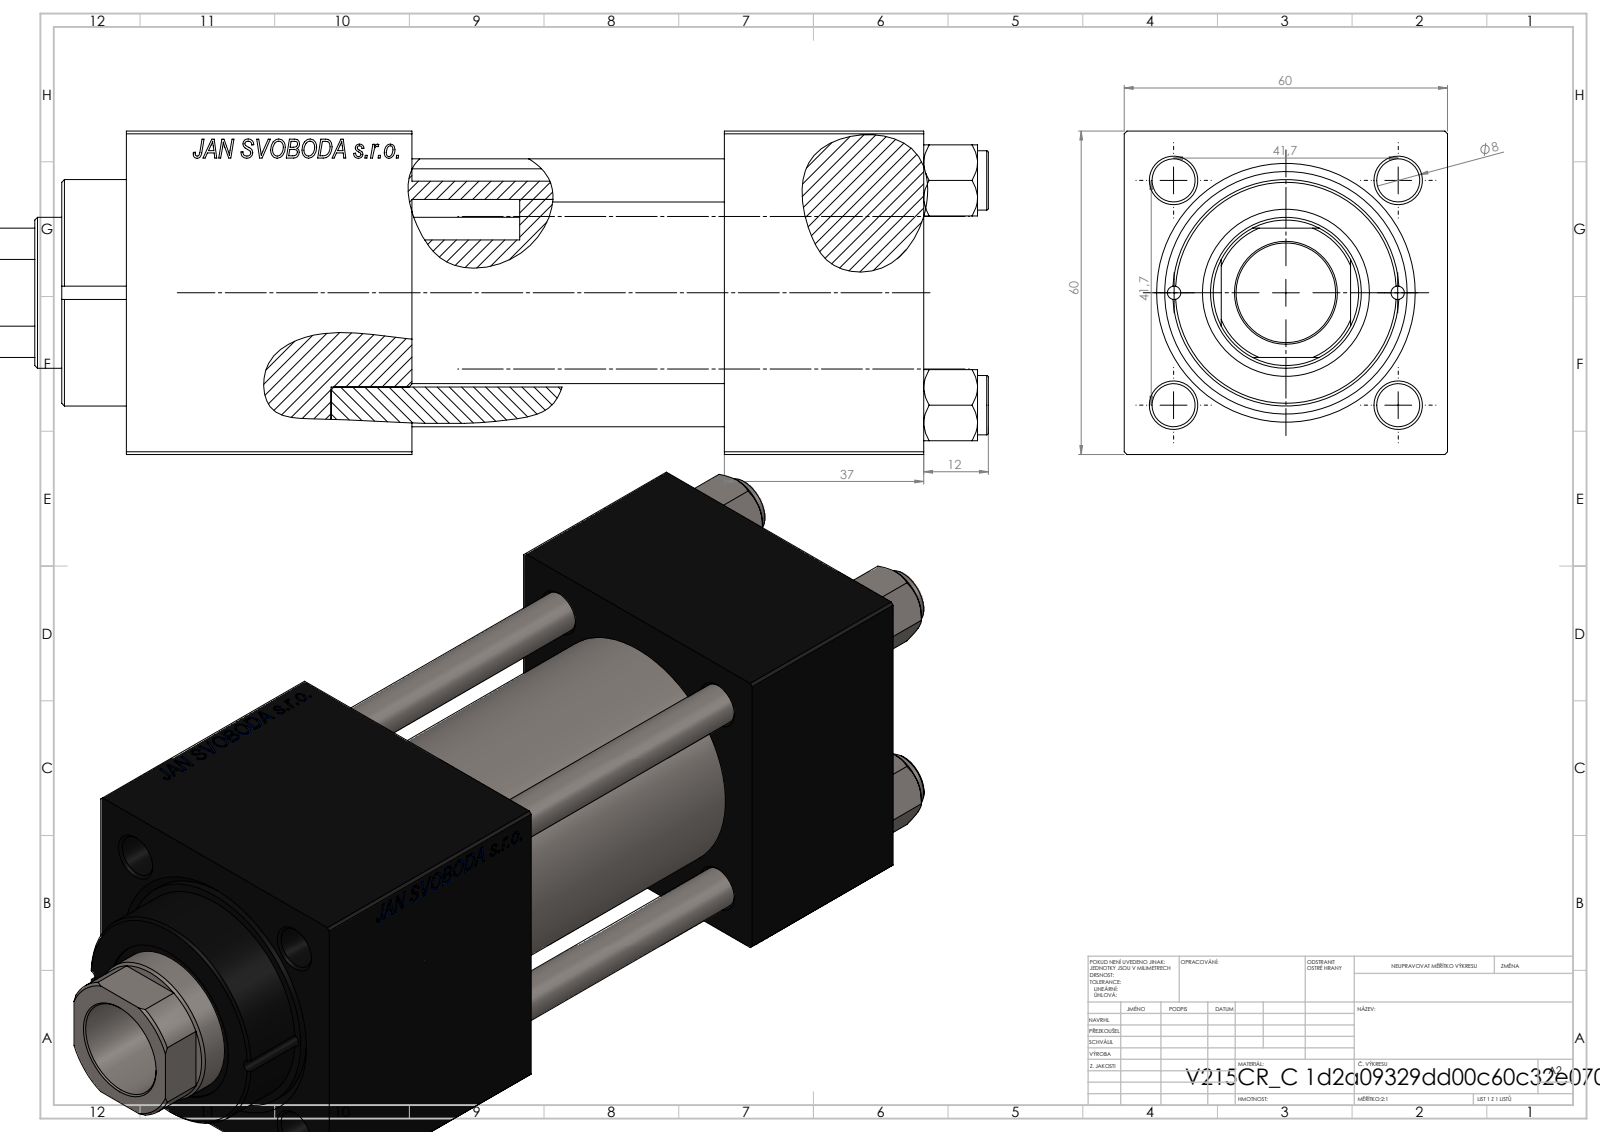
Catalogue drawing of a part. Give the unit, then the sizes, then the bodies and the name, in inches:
Units: inches
Overall size (bounding box): 7.283 × 2.362 × 2.362
Round holes (diameter × count): ⌀0.315 ×4, ⌀0.098 ×2, ⌀0.276 ×2, ⌀0.656 ×2, ⌀0.945 ×2, ⌀0.728 ×1, ⌀1.102 ×1, ⌀1.22 ×1, ⌀1.575 ×1, ⌀1.772 ×1
Round bosses / shafts (diameter × count): ⌀0.433 ×4, ⌀1.811 ×1, ⌀1.654 ×1
Partial cylindrical surfaces — rounded edges, fillets, slot ends (radius × count): R0.531 ×1
Main face-to-face distances: 2.362, 1.457, 2.283, 3.74, 2.087, 4.697, 3.24, 0.957, 5.827, 4.37
Hole centre spacings: 0.821, 1.161, 1.642, 1.832, 0.817, 2.322, 1.634, 3.642
Volume: 25.88 in³ · Surface area: 172.9 in²
Bodies: 11 solids, 1154 faces (528 planar, 90 cylindrical, 536 other)
Part name (STEP PRODUCT): V215CR_C_Body; V215CR_C_TYCINKA; V215_VC_A; V215CR_VCP_C (+1 more)
STEP written by: SolidWorks 2019 (CONFIG_CONTROL_DESIGN)
